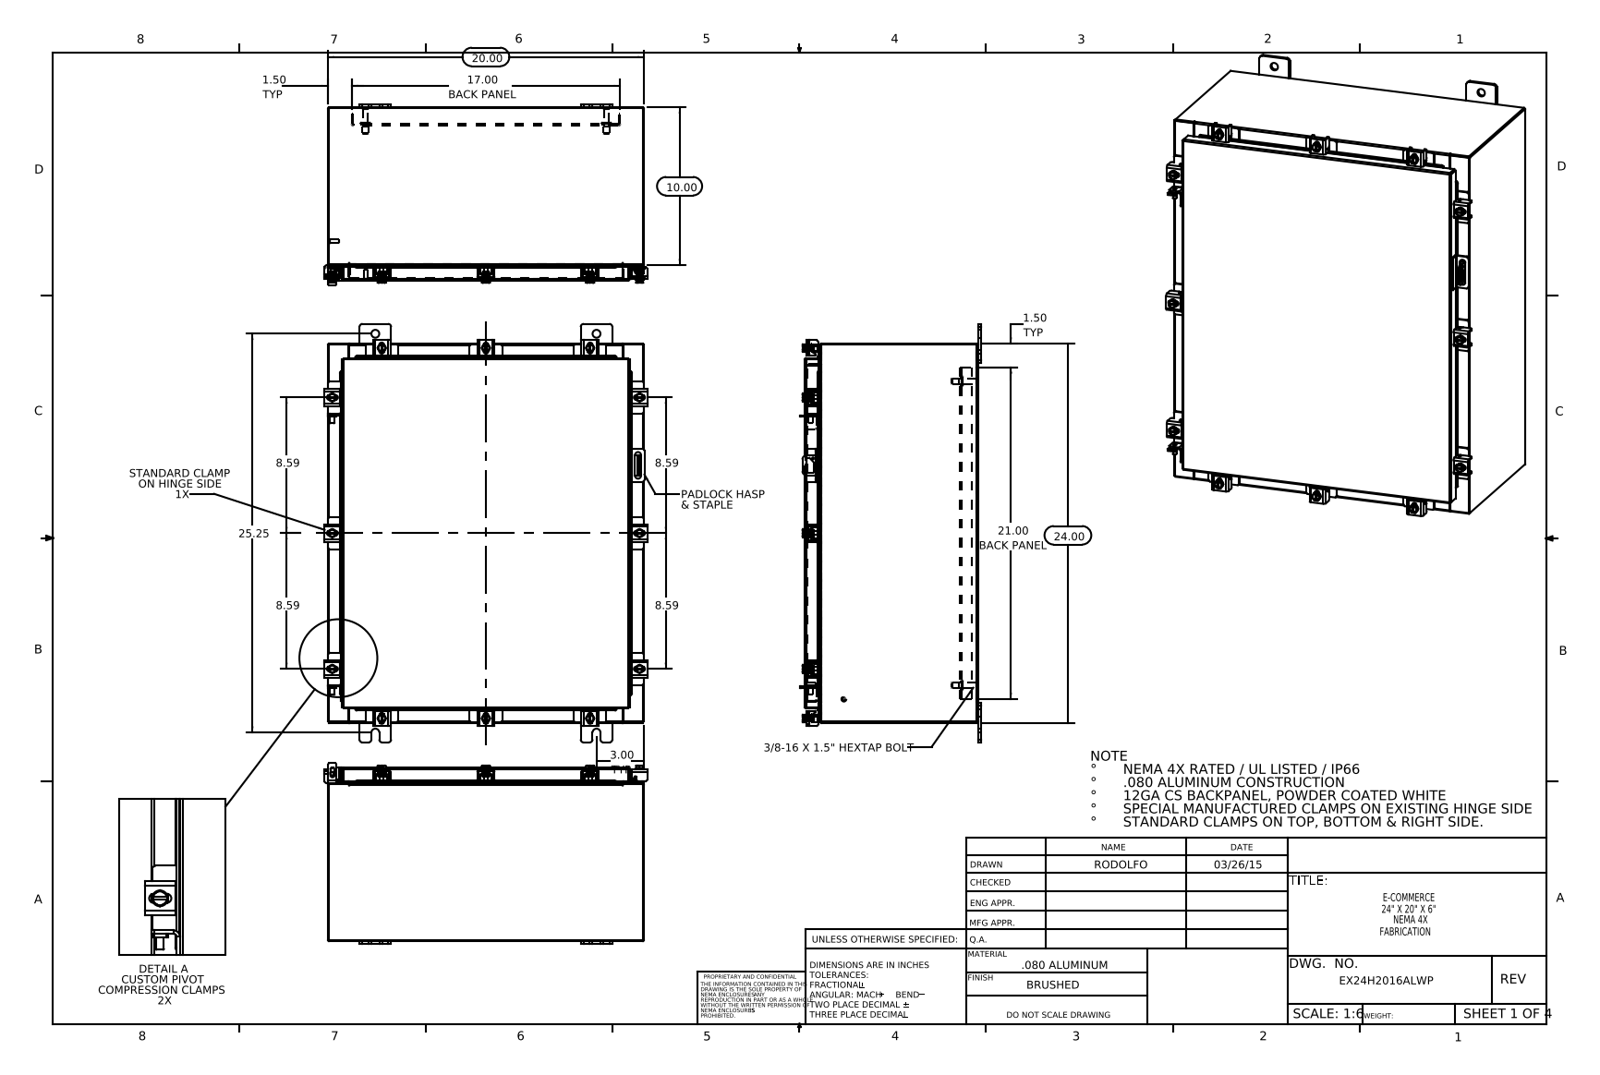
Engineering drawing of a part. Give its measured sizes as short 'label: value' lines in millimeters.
name: 22101002_RTP29; EX24H2016ALWP; EX24H2016ALWP Body; EX24H2016ALWP Cover (+8 more)
written by: SolidWorks 2014 (CONFIG_CONTROL_DESIGN)
unit: mm
bodies: 81 solids, 2018 faces (1075 planar, 783 cylindrical, 160 other)
size: 673.1 × 518.7 × 290.9
volume: 3 282 000 mm³; area: 3 250 000 mm²
holes: 12× ⌀5.4, 12× ⌀6.6, 8× ⌀12.7, 1× ⌀3.2, 1× ⌀6.4
bosses: 12× ⌀12.7, 12× ⌀6.4, 10× ⌀10.1, 4× ⌀15.9, 4× ⌀9.5, 4× ⌀8.4, 2× ⌀8, 2× ⌀6
rounds: 54× R1.5, 24× R0.3, 24× R3.6, 24× R4.8, 22× R2.2, 22× R3, 18× R2.3, 17× R1.3
face distances: 1.9, 276.9, 506.1, 278.8, 275, 607.7, 2.6, 25.4, 27.3, 249.6
hole spacings: 59.4, 112.5, 167.5, 218.3, 259.5, 308.3, 386.9, 422.1
